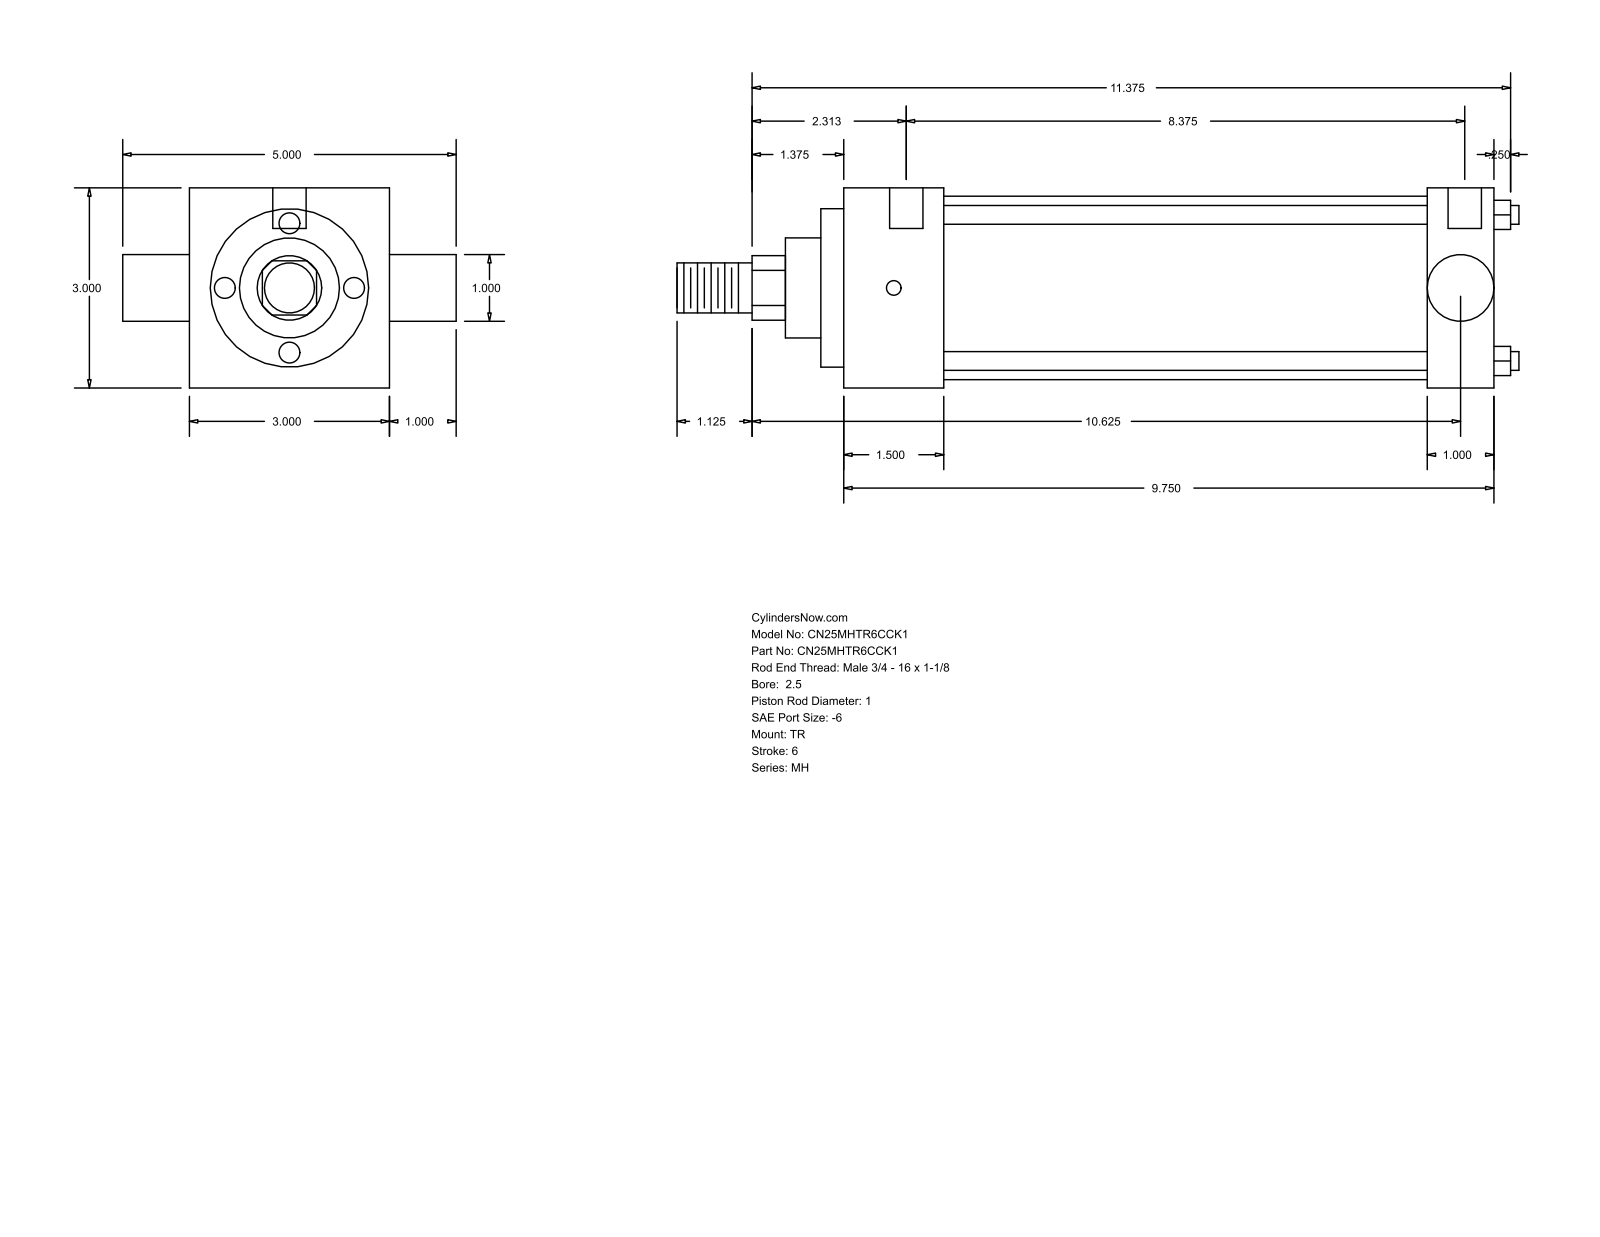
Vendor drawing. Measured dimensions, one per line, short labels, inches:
name: MH_TR__0250_1
written by: GSSL Pune (CONFIG_CONTROL_DESIGN)
unit: in
bodies: 0 solids, 86 faces (61 planar, 25 cylindrical, 0 other)
size: 12.625 × 5 × 3
holes: 3× ⌀0.219, 2× ⌀0.5
bosses: 4× ⌀0.281, 1× ⌀2.75, 1× ⌀2.375, 1× ⌀1.5, 1× ⌀1, 1× ⌀0.998, 1× ⌀0.75
rounds: 1× R0.484
face distances: 3, 9.75, 1, 1.5, 8.25, 8.75, 7.25, 0.344, 1.844, 9.094
hole spacings: 0.125, 0.187, 8.375, 8.5, 8.562, 8.687
